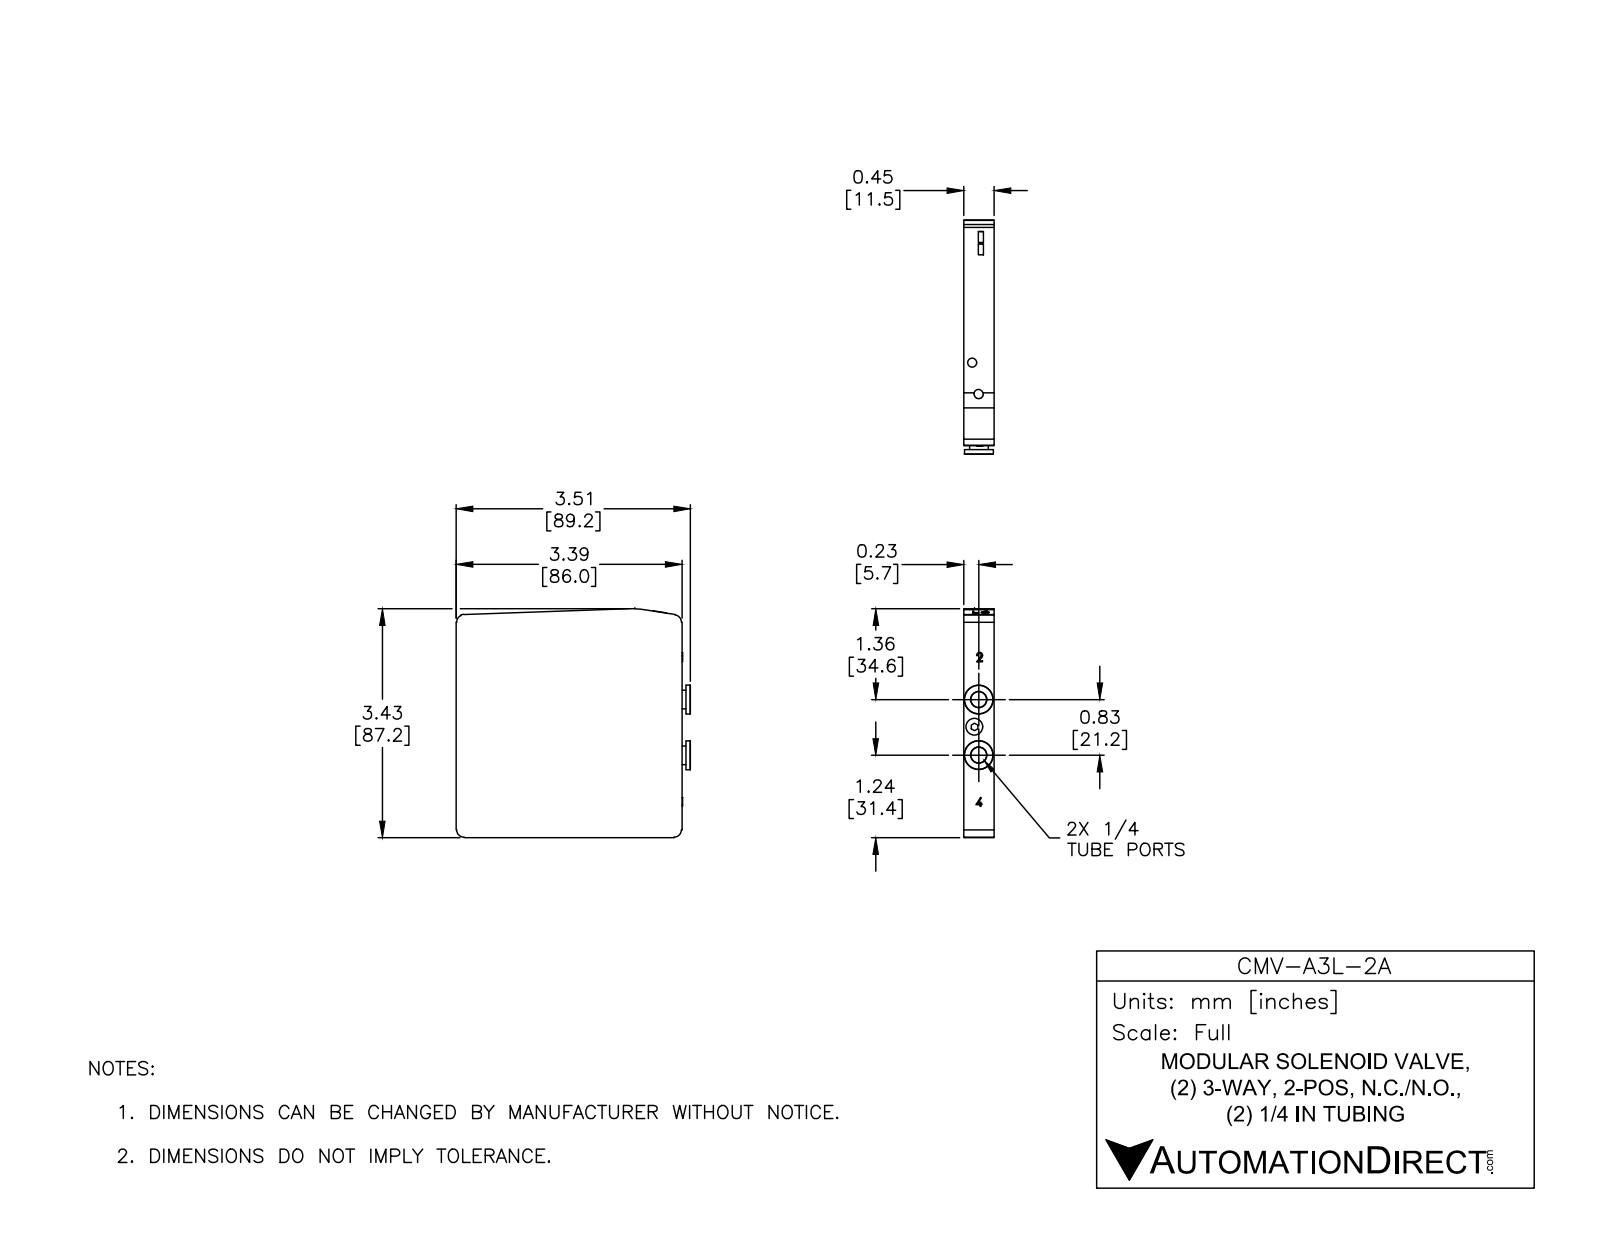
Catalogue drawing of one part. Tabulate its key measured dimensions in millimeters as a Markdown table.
| quantity | value |
| --- | --- |
| part name | CMV-A3L-2A |
| STEP written by | SolidWorks 2017 (AUTOMOTIVE_DESIGN) |
| units | millimeters |
| bodies | 1 solid, 138 faces (80 planar, 50 cylindrical, 8 other) |
| overall size | 89.2 × 87.22 × 11.5 |
| volume | 85 213 mm³ |
| surface area | 19 252 mm² |
| round holes (diameter × count) | 3.5 × 2, 6 × 2, 6.4 × 1 |
| round bosses / shafts (diameter × count) | 11 × 2, 7.1 × 2 |
| partial cylindrical surfaces (radius × count) | 2.8 × 4, 1.67 × 2, 0.17 × 1, 0.55 × 1, 0.61 × 1, 0.88 × 1, 0.92 × 1, 0.92 × 1 |
| main face-to-face distances | 11.5, 86, 1.7, 3.2, 89.2, 87.5, 1.5, 85.8, 2.5, 3.4 |
| hole center spacings | 10.54, 10.93, 12.14, 21.2 |
